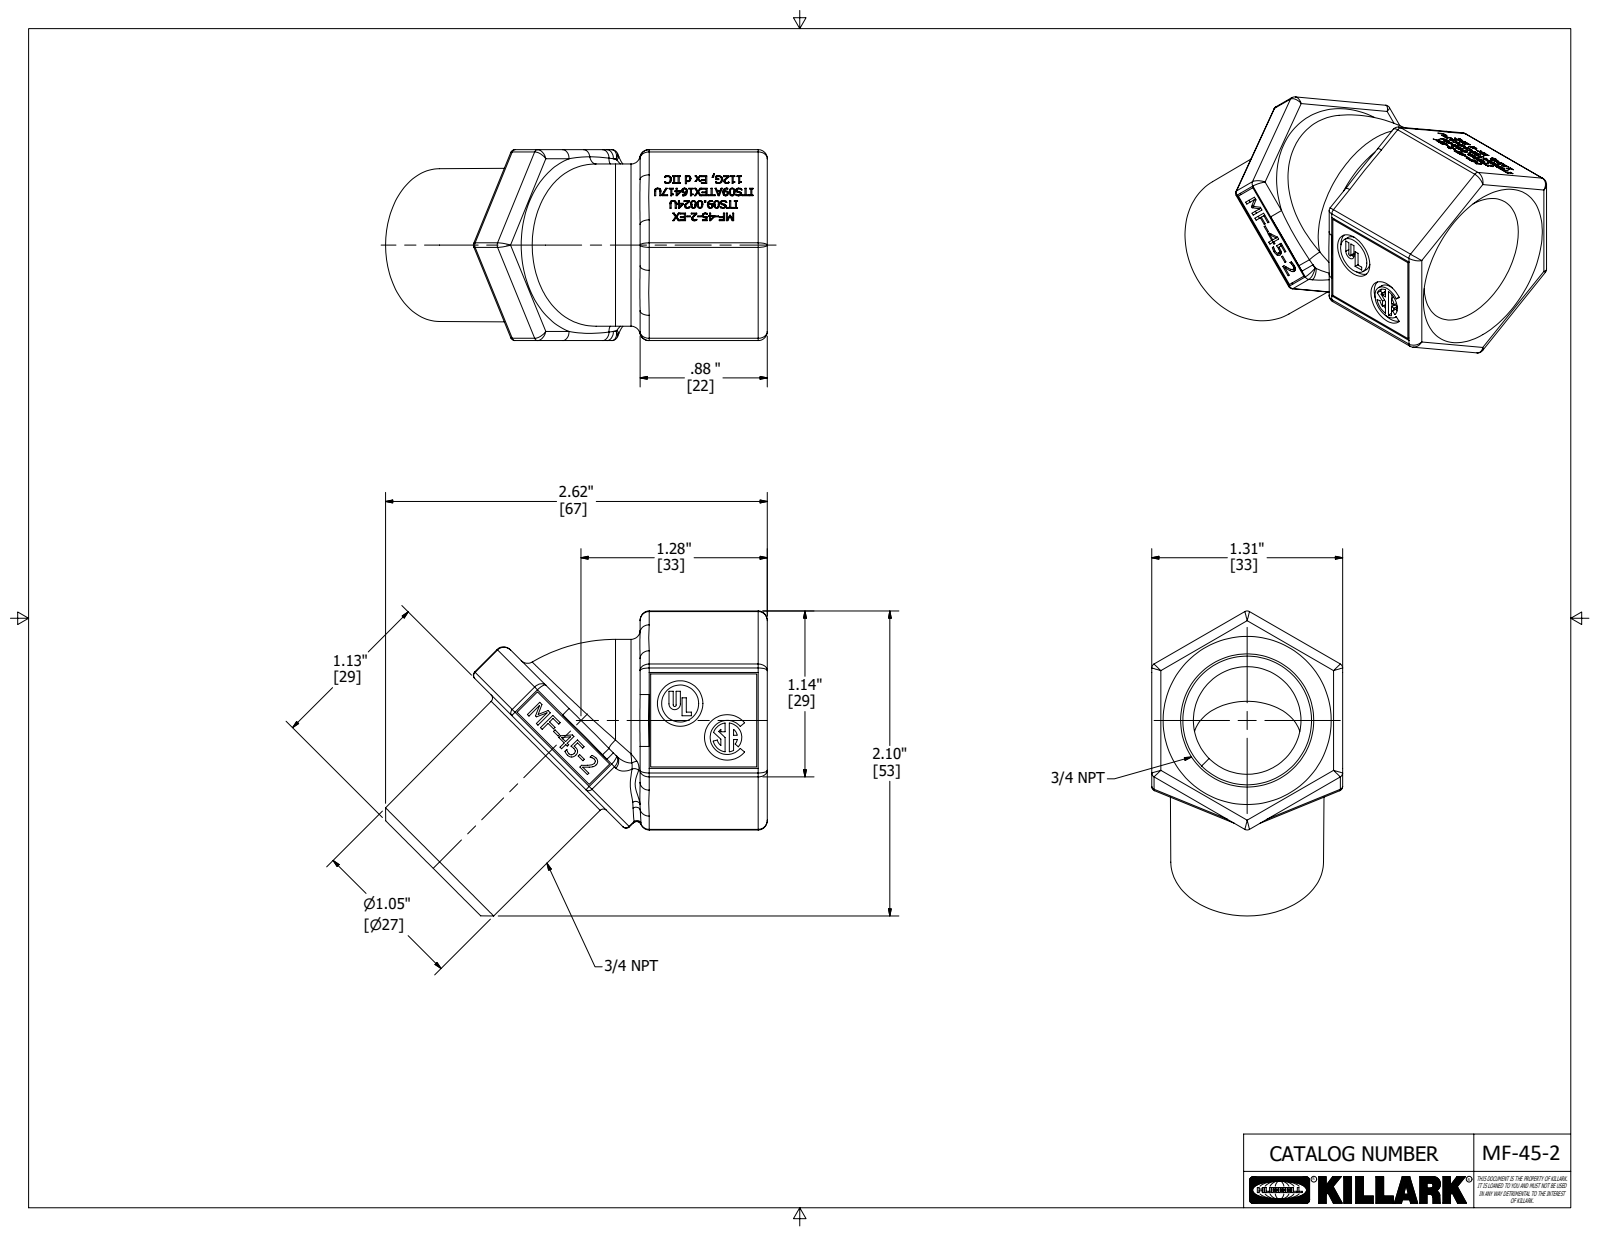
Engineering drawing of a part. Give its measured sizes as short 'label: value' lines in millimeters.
name: MF-45-2
written by: Autodesk Inventor 2020 (AUTOMOTIVE_DESIGN)
unit: mm
bodies: 1 solid, 1462 faces (917 planar, 58 cylindrical, 487 other)
size: 66.7 × 53.3 × 33.4
volume: 28 220 mm³; area: 13 160 mm²
holes: 1× ⌀8
bosses: 1× ⌀6.5
rounds: 18× R0.8, 18× R1.6, 1× R0.3, 1× R1, 1× R1.8, 1× R2.5, 1× R3, 1× R4
face distances: 33.4, 0.8, 32.5, 33.3, 28.6, 1.8, 31.7, 16.5, 1.6, 5.3
